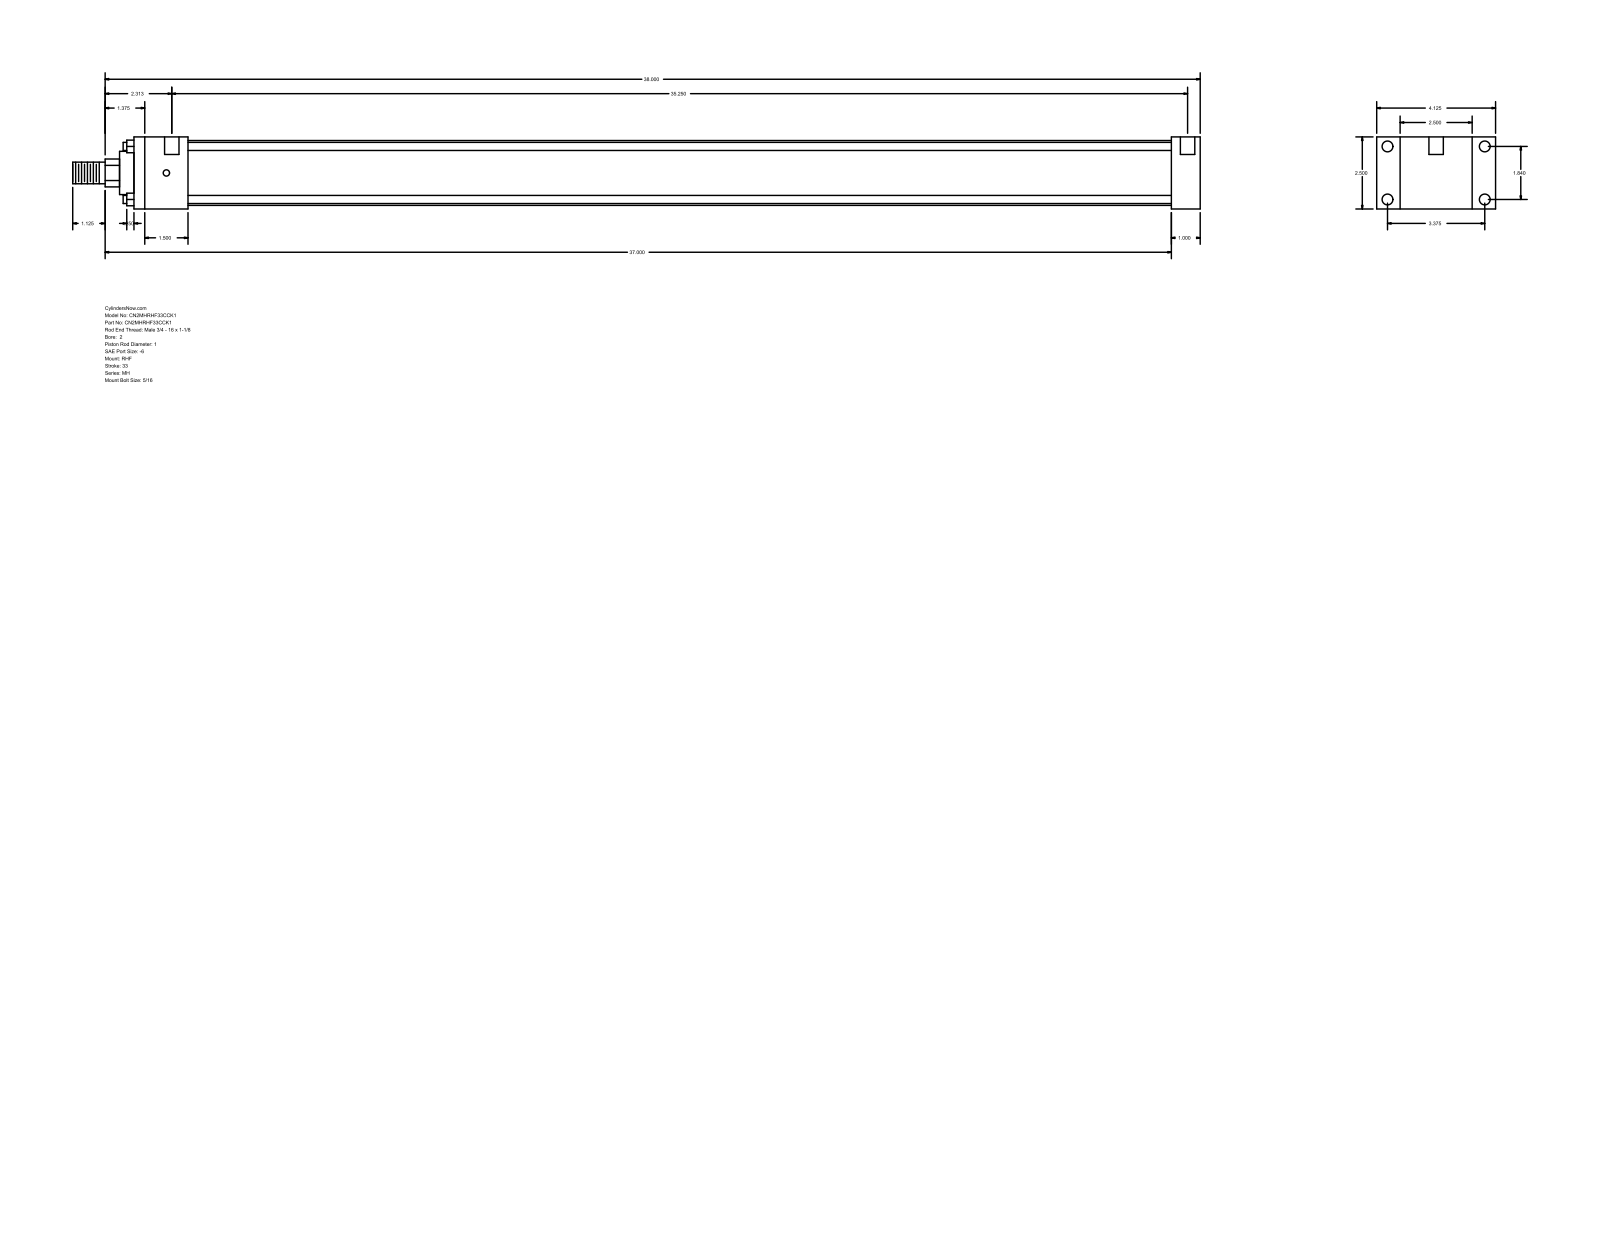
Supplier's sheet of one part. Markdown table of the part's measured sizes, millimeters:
| quantity | value |
| --- | --- |
| part name | MH_RHF__0200_1 |
| STEP written by | GSSL Pune (CONFIG_CONTROL_DESIGN) |
| units | millimeters |
| bodies | 0 solids, 88 faces (60 planar, 28 cylindrical, 0 other) |
| overall size | 993.77 × 104.78 × 63.5 |
| round holes (diameter × count) | 5.56 × 4, 9.53 × 4, 12.7 × 2 |
| round bosses / shafts (diameter × count) | 7.14 × 4, 57.15 × 1, 38.1 × 1, 25.4 × 1, 19.05 × 1 |
| partial cylindrical surfaces (radius × count) | 12.29 × 1 |
| main face-to-face distances | 63.5, 25.4, 20.64, 84.14, 939.8, 914.4, 104.78, 47.63, 866.77, 892.17 |
| hole center spacings | 46.74, 85.72, 97.63, 903.28, 3.17, 4.76, 895.35, 898.52 |
